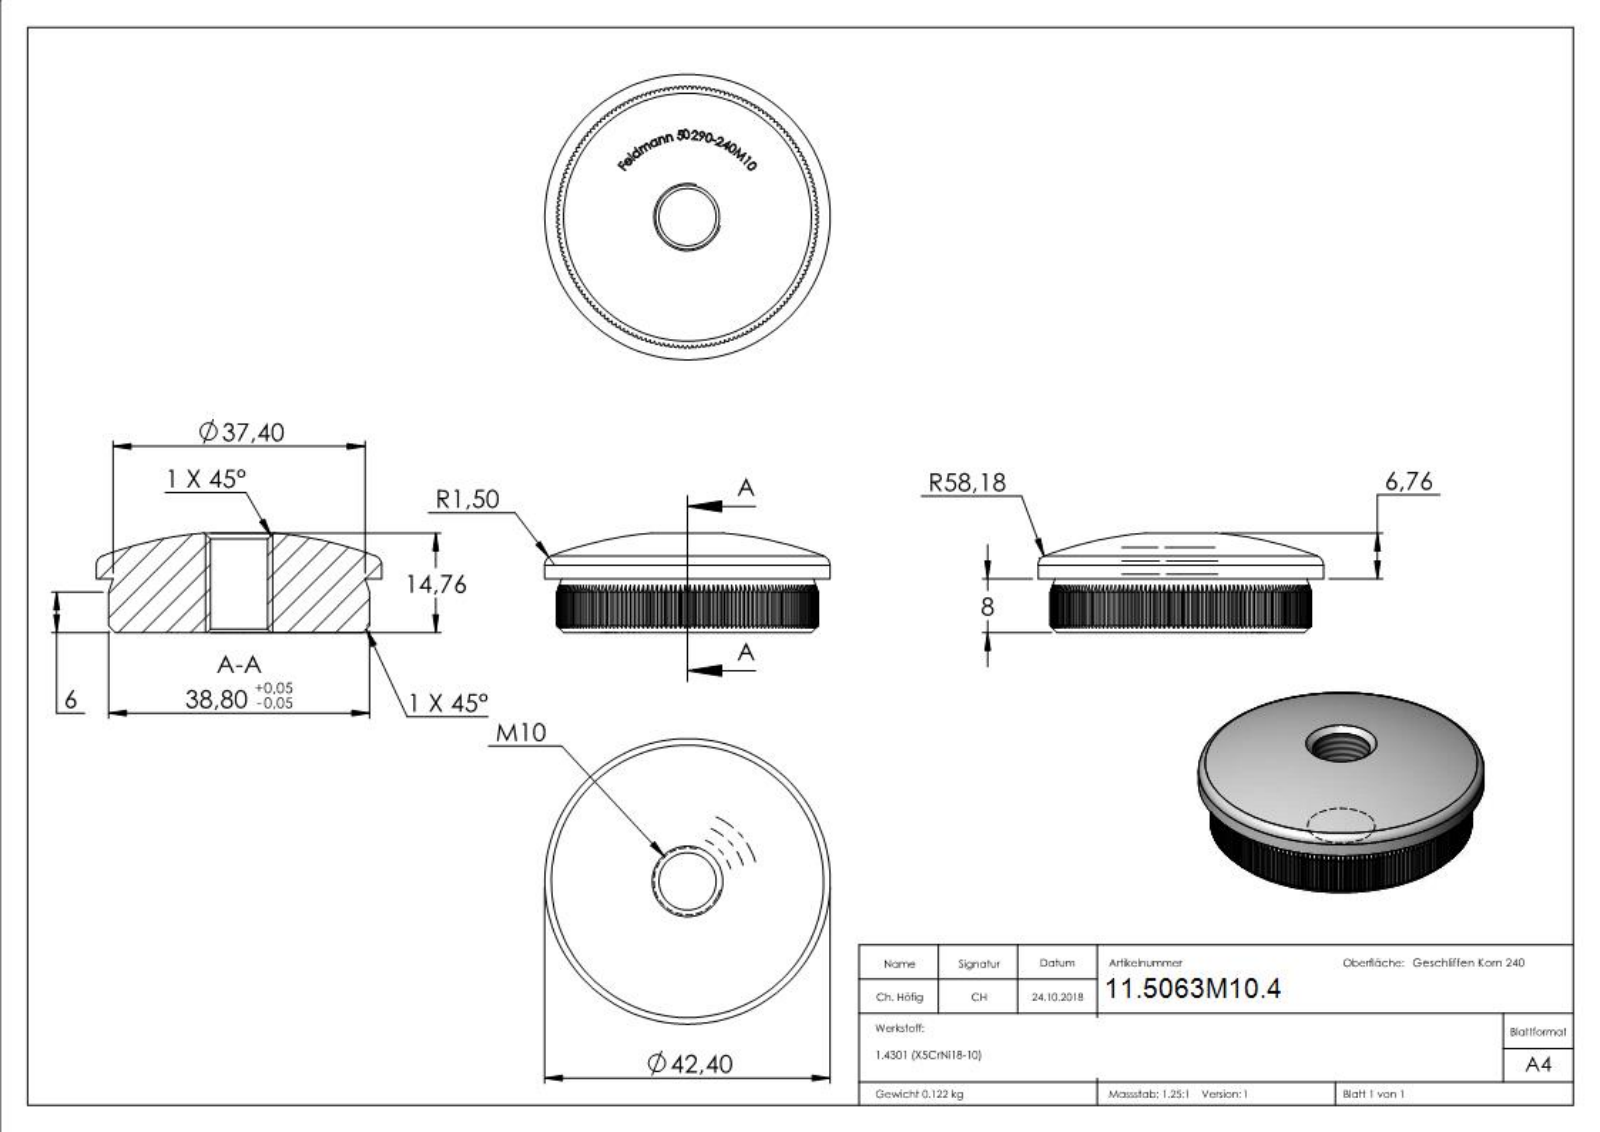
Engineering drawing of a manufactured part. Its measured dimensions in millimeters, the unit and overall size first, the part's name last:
Units: millimetres
Overall size (bounding box): 42.4 × 42.4 × 14.76
Round holes (diameter × count): ⌀8.5 ×1
Round bosses / shafts (diameter × count): ⌀42.4 ×1
Partial cylindrical surfaces — rounded edges, fillets, slot ends (radius × count): R19.4 ×1
Main face-to-face distances: 8, 19.06, 19.04, 19.08, 7.9, 19.02, 0.66, 0.54, 0.67, 0.79
Volume: 15 453 mm³ · Surface area: 4 886 mm²
Bodies: 1 solid, 753 faces (472 planar, 174 cylindrical, 107 other)
Part name (STEP PRODUCT): 50290-240M10
STEP written by: SolidWorks 2015 (CONFIG_CONTROL_DESIGN)
